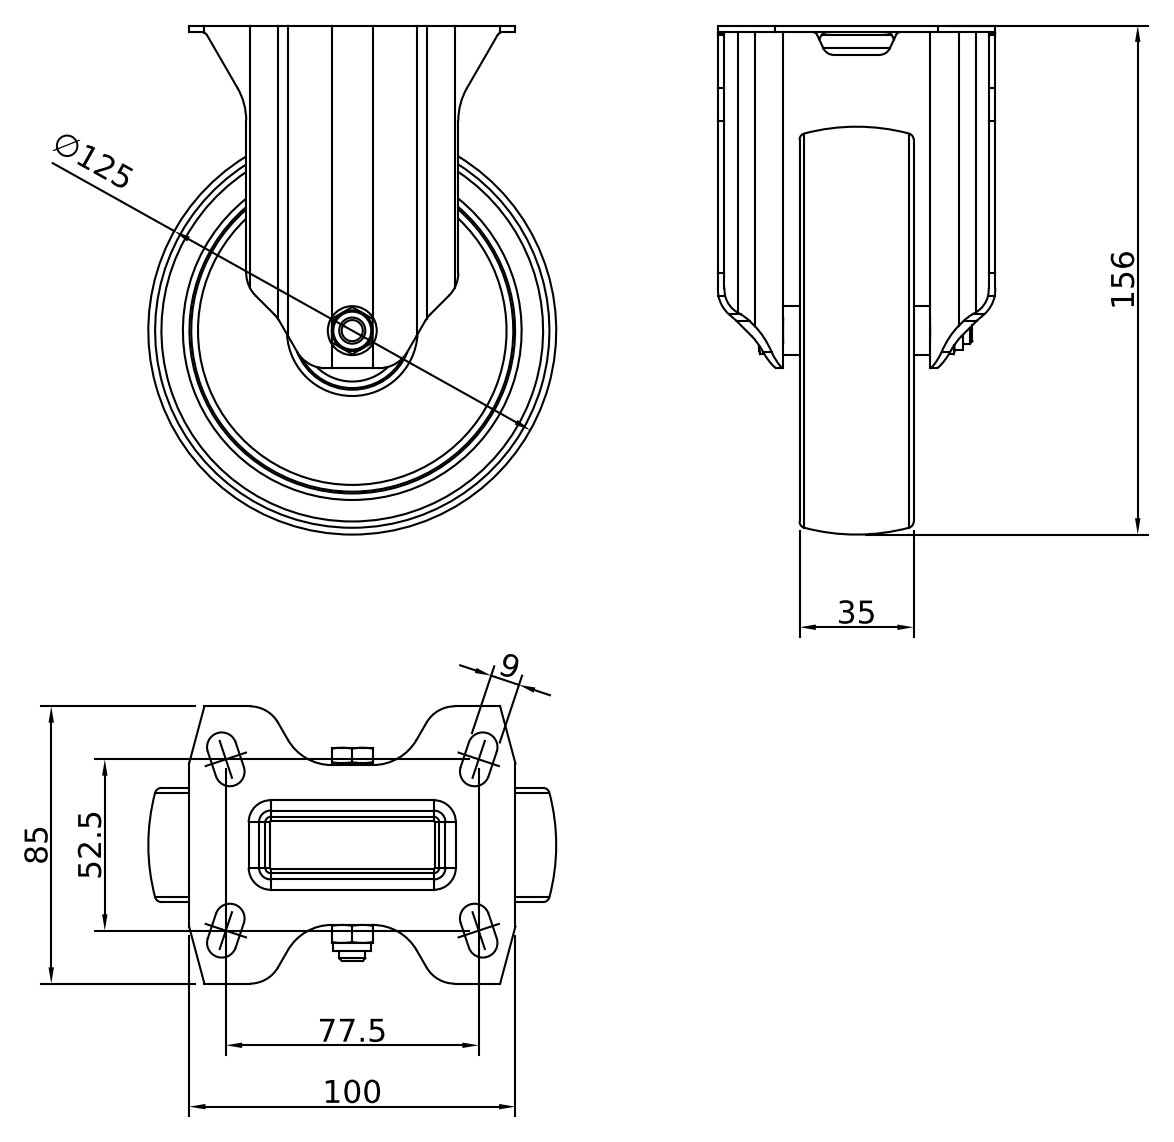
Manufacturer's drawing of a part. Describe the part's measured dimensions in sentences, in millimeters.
The part is named "CRUST0000042". Its 3-D file was written by "Autodesk Inventor 2022 (AUTOMOTIVE_DESIGN)". It is 3 solids with 224 faces: 97 planar, 73 cylindrical and 54 other. Overall it measures 156 by 125 by 85 millimeters. Its volume is 277 107 cubic millimeters and its surface area 97 394 square millimeters. Round holes: 1 of diameter 15. Round bosses or shafts: 1 of diameter 11.63, 1 of diameter 8. Partial cylindrical surfaces (rounded edges, fillets, slot ends): 10 of radius 10, 8 of radius 1.5, 8 of radius 3.5, 8 of radius 4.5, 4 of radius 7, 4 of radius 8, 4 of radius 15.5, 4 of radius 17.5. The main face-to-face distances are 2, 7, 5, 35, 40, 42, 47, 3.92, 65, 18.
